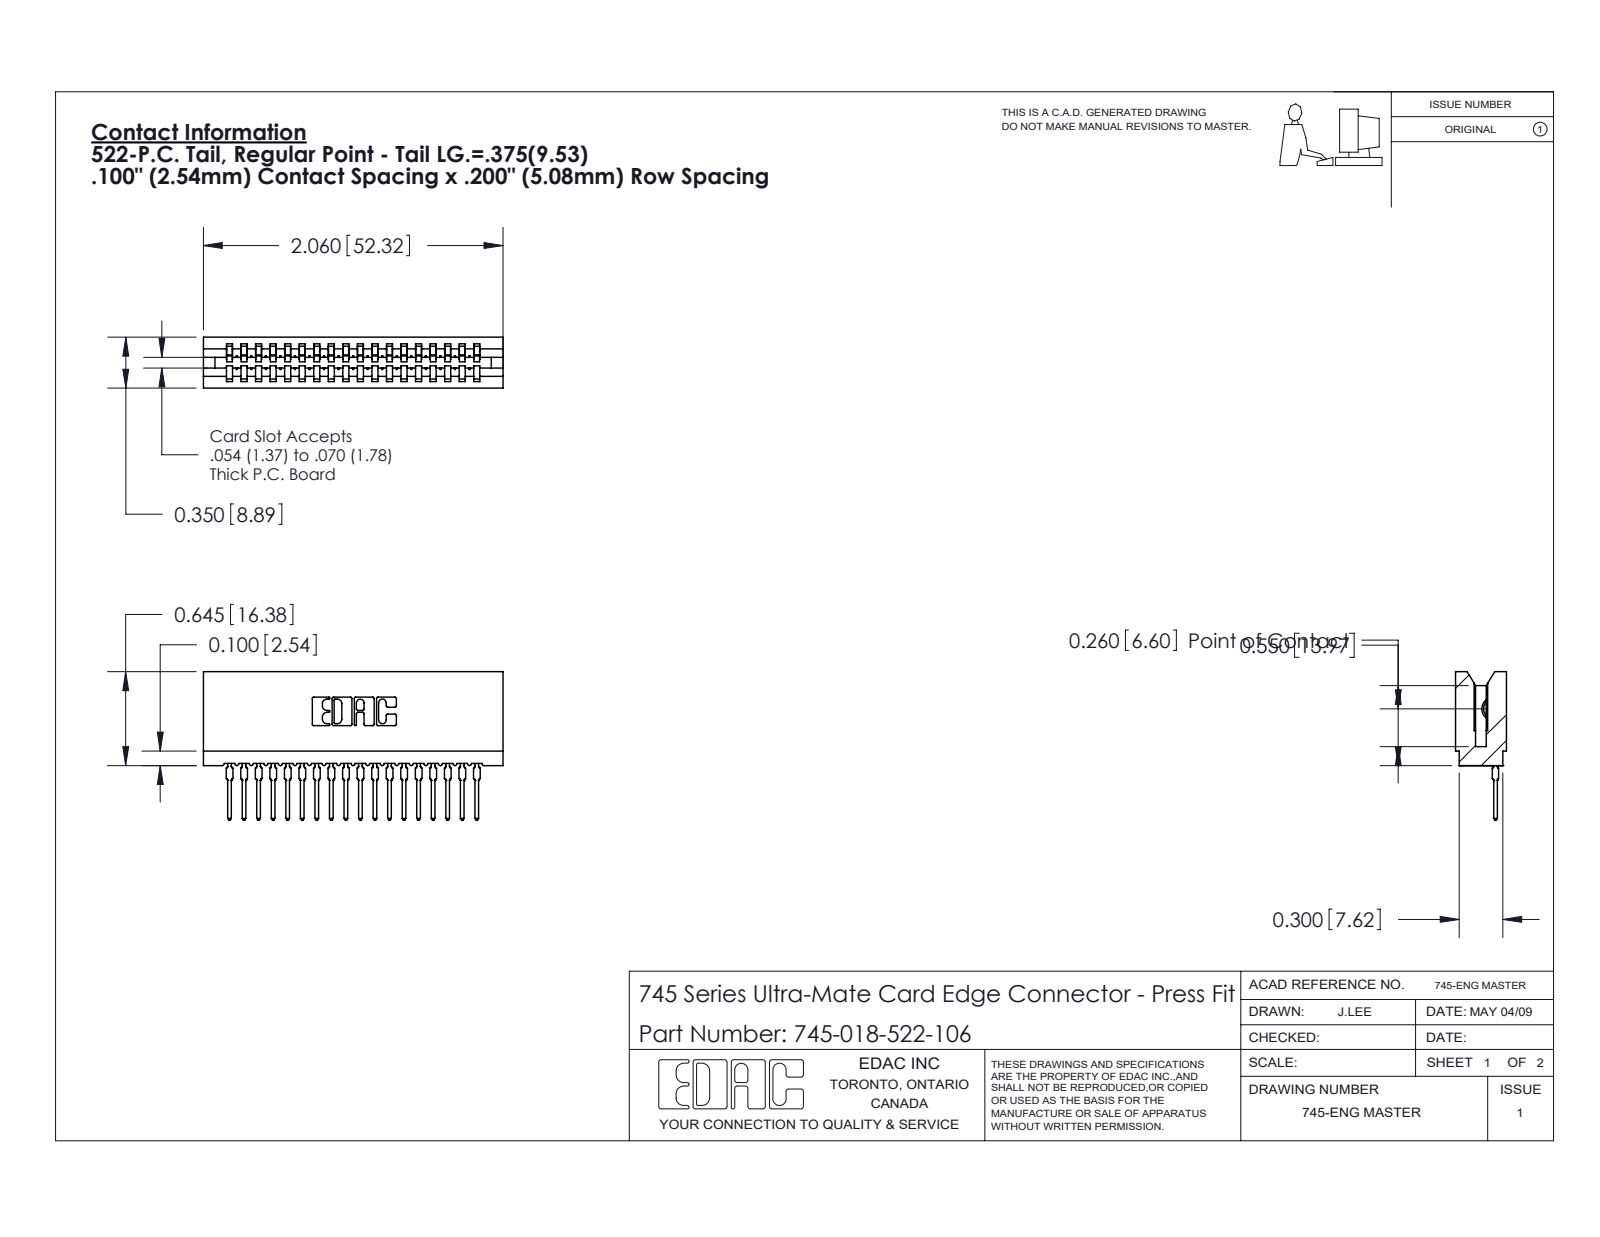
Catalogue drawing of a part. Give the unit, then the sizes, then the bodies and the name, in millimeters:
Units: millimetres
Overall size (bounding box): 52.3 × 25.9 × 8.9
Partial cylindrical surfaces — rounded edges, fillets, slot ends (radius × count): R0.4 ×36, R0.5 ×36, R0.3 ×22, R0.2 ×6, R0.8 ×6, R0.1 ×4, R0.3 ×4, R0.7 ×3
Main face-to-face distances: 2.5, 5.1, 7.6, 10.2, 12.7, 15.2, 8.9, 17.8, 20.3, 3.5
Volume: 4 670 mm³ · Surface area: 8 310 mm²
Bodies: 19 solids, 2112 faces (1262 planar, 382 cylindrical, 468 other)
Part name (STEP PRODUCT): 745 Part_Insulator Option - 06; 745-018-522-106; 745-292-001_522
STEP written by: SolidWorks 2020 (CONFIG_CONTROL_DESIGN)
